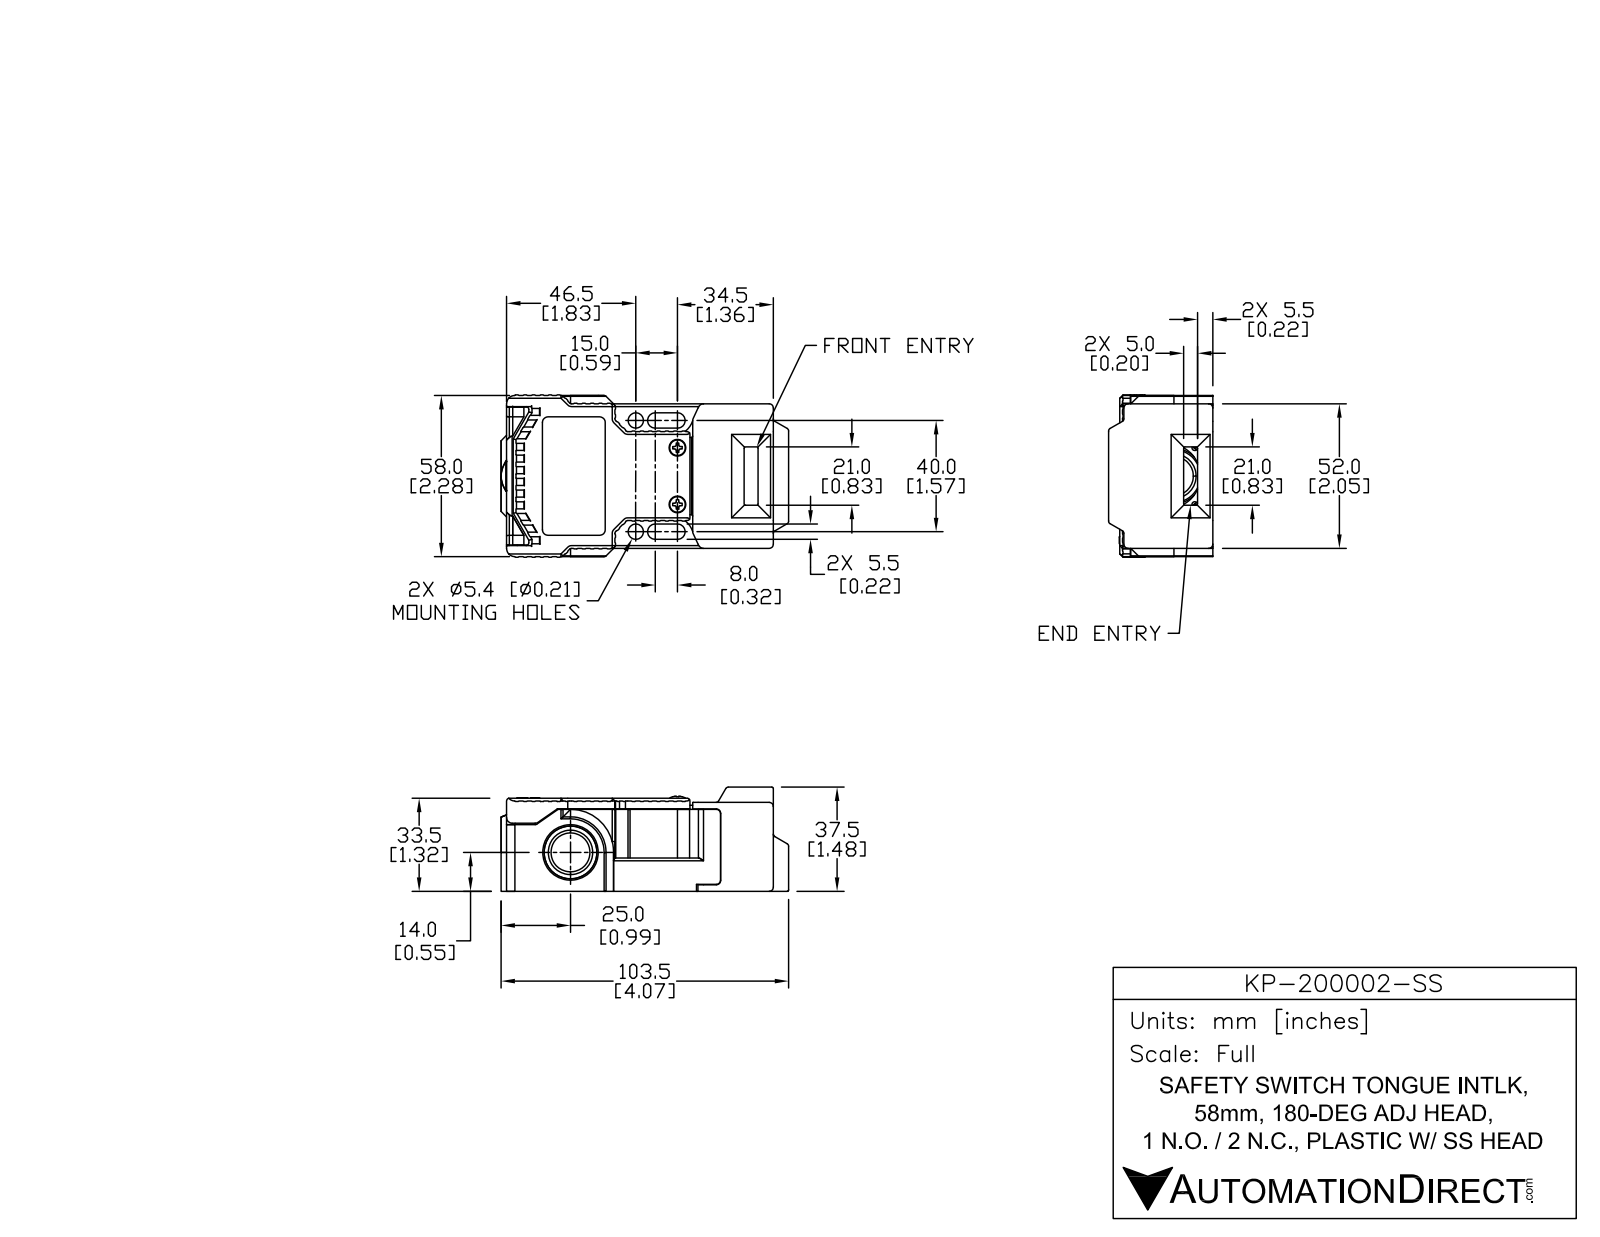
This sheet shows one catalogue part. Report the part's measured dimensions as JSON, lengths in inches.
{"part_name": "KP-200002-SS", "step_written_by": "SolidWorks 2013 (AUTOMOTIVE_DESIGN)", "units": "inches", "bodies": {"solids": 1, "faces": 297, "planar": 177, "cylindrical": 81, "other": 39}, "overall_size": [3.967, 2.283, 1.476], "volume_in3": 9.627, "surface_area_in2": 39.45, "round_holes": [[0.213, 2], [0.761, 1], [0.787, 1]], "round_bosses_or_shafts": [[0.22, 2]], "partial_cylinders_radius": [[0.039, 36], [0.079, 13], [0.108, 4], [0.157, 3], [0.089, 2], [0.118, 2], [0.128, 2], [0.197, 2]], "face_to_face_distances": [1.319, 2.047, 0.118, 2.165, 1.317, 3.78, 0.041, 1.358, 0.039, 0.504], "hole_center_spacings": [1.575]}
